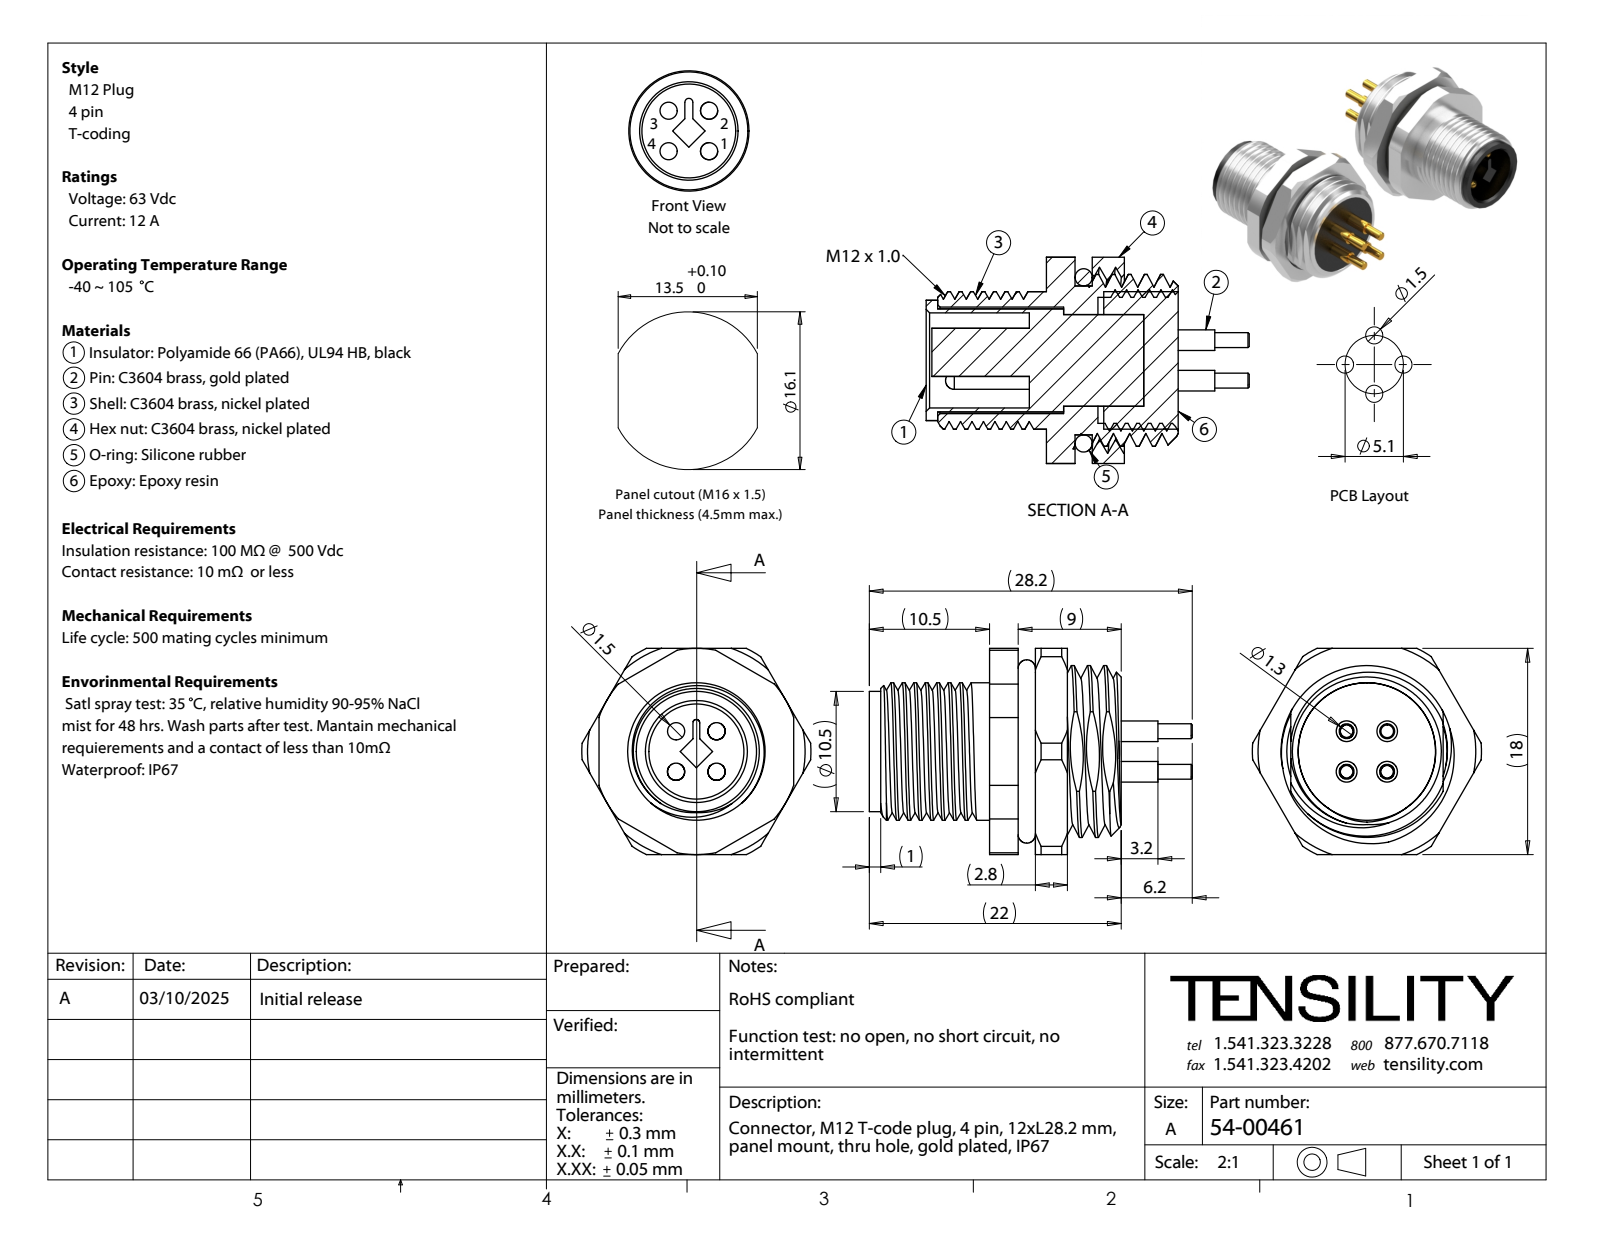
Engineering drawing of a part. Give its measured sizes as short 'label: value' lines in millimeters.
name: 54-00461-01; 54-00461-05; 54-00461-03; 54-00461-02 (+3 more)
written by: SolidWorks 2021 (CONFIG_CONTROL_DESIGN)
unit: mm
bodies: 9 solids, 324 faces (80 planar, 150 cylindrical, 94 other)
size: 28.2 × 20 × 18
volume: 3 016 mm³; area: 5 763 mm²
holes: 4× ⌀1.5, 1× ⌀8, 1× ⌀8.3, 1× ⌀9.3, 1× ⌀11, 1× ⌀14
bosses: 4× ⌀1.8, 4× ⌀1.3, 1× ⌀13, 1× ⌀12, 1× ⌀10.5, 1× ⌀9
rounds: 1× R0.3, 1× R7.5, 1× R9, 1× R10
face distances: 2.5, 4, 1.5, 3, 9, 11.5, 6, 4.5, 1, 18
hole spacings: 2.5, 3.54, 5.01
